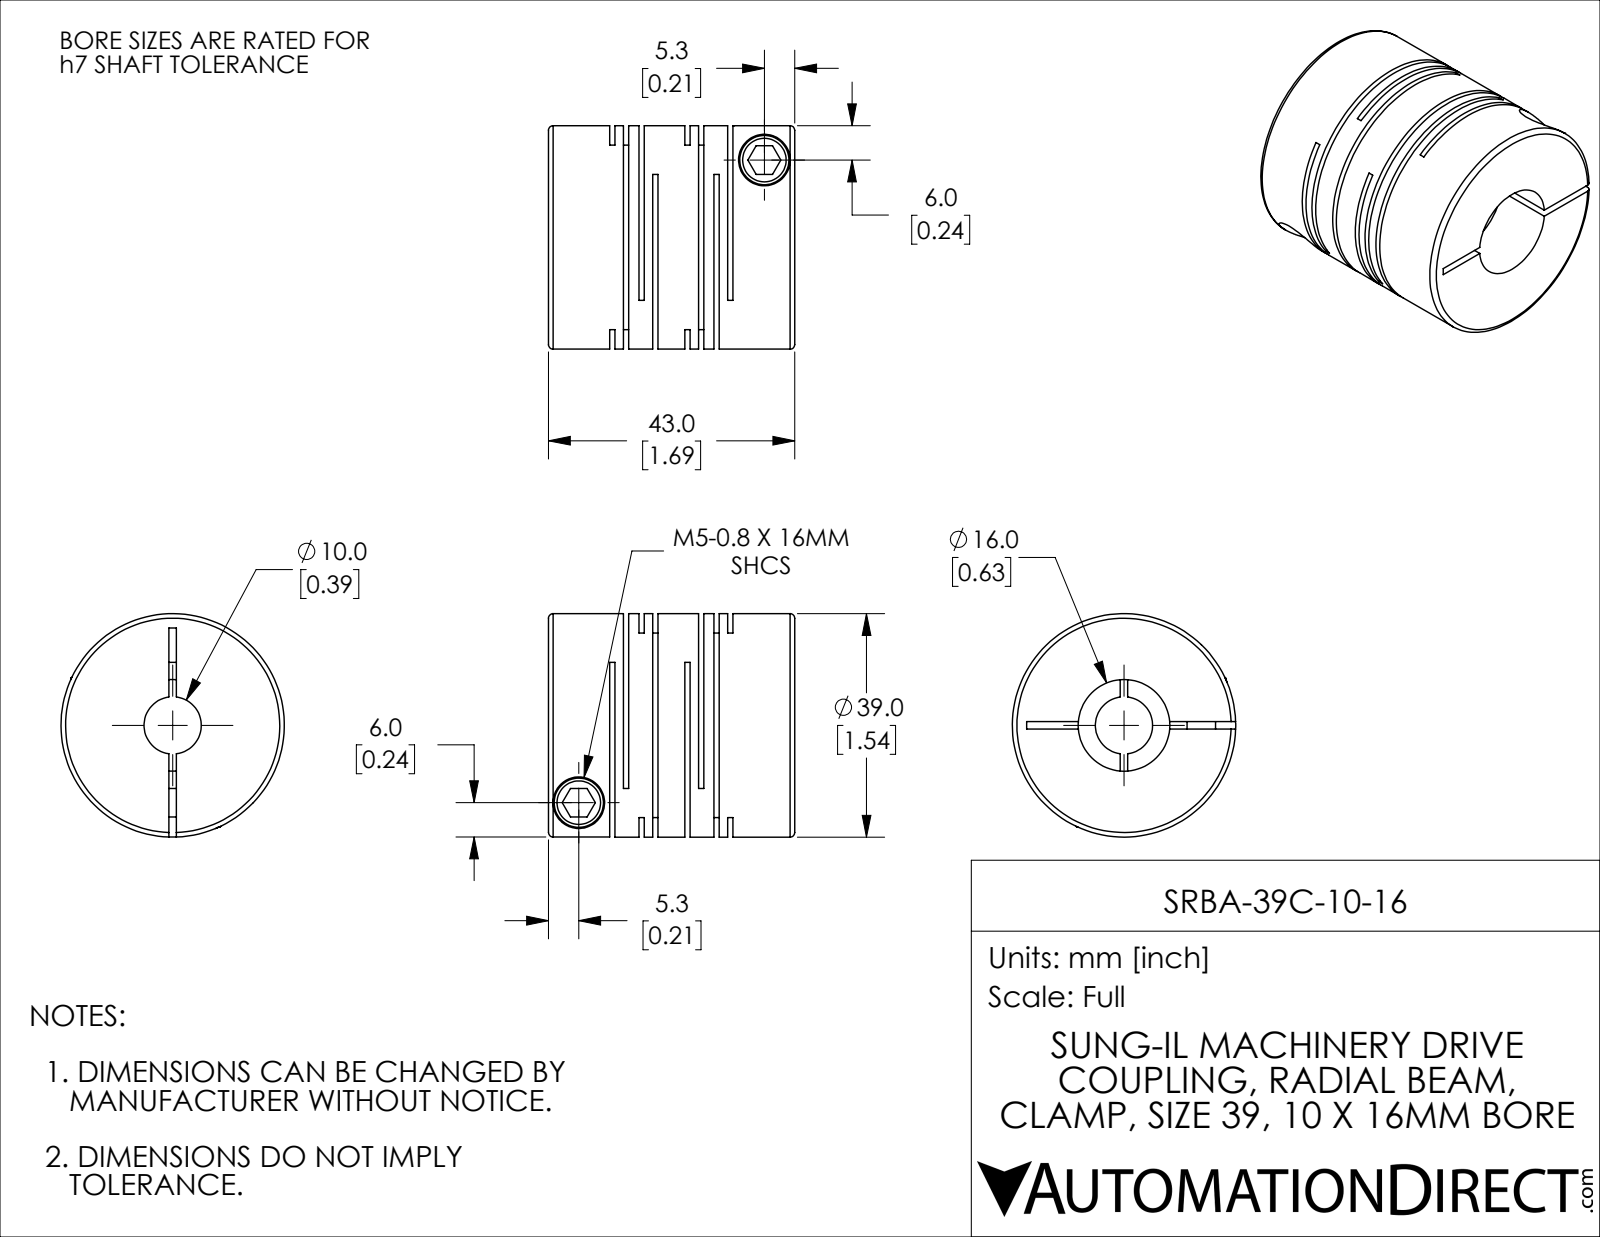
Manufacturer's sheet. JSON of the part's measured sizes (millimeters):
{"part_name": "SRBA-39C-10-16", "step_written_by": "SolidWorks 2021 (CONFIG_CONTROL_DESIGN)", "units": "millimeters", "bodies": {"solids": 1, "faces": 114, "planar": 60, "cylindrical": 42, "other": 12}, "overall_size": [43, 39, 39], "volume_mm3": 36571, "surface_area_mm2": 23101, "round_holes": [[5, 2], [9, 2], [10, 1], [16, 1]], "round_bosses_or_shafts": [[8.6, 2], [39, 1]], "face_to_face_distances": [13.1, 0.92, 2.4, 5.1, 10.7, 14.02, 18.2, 3.32, 15.5, 1.48]}
